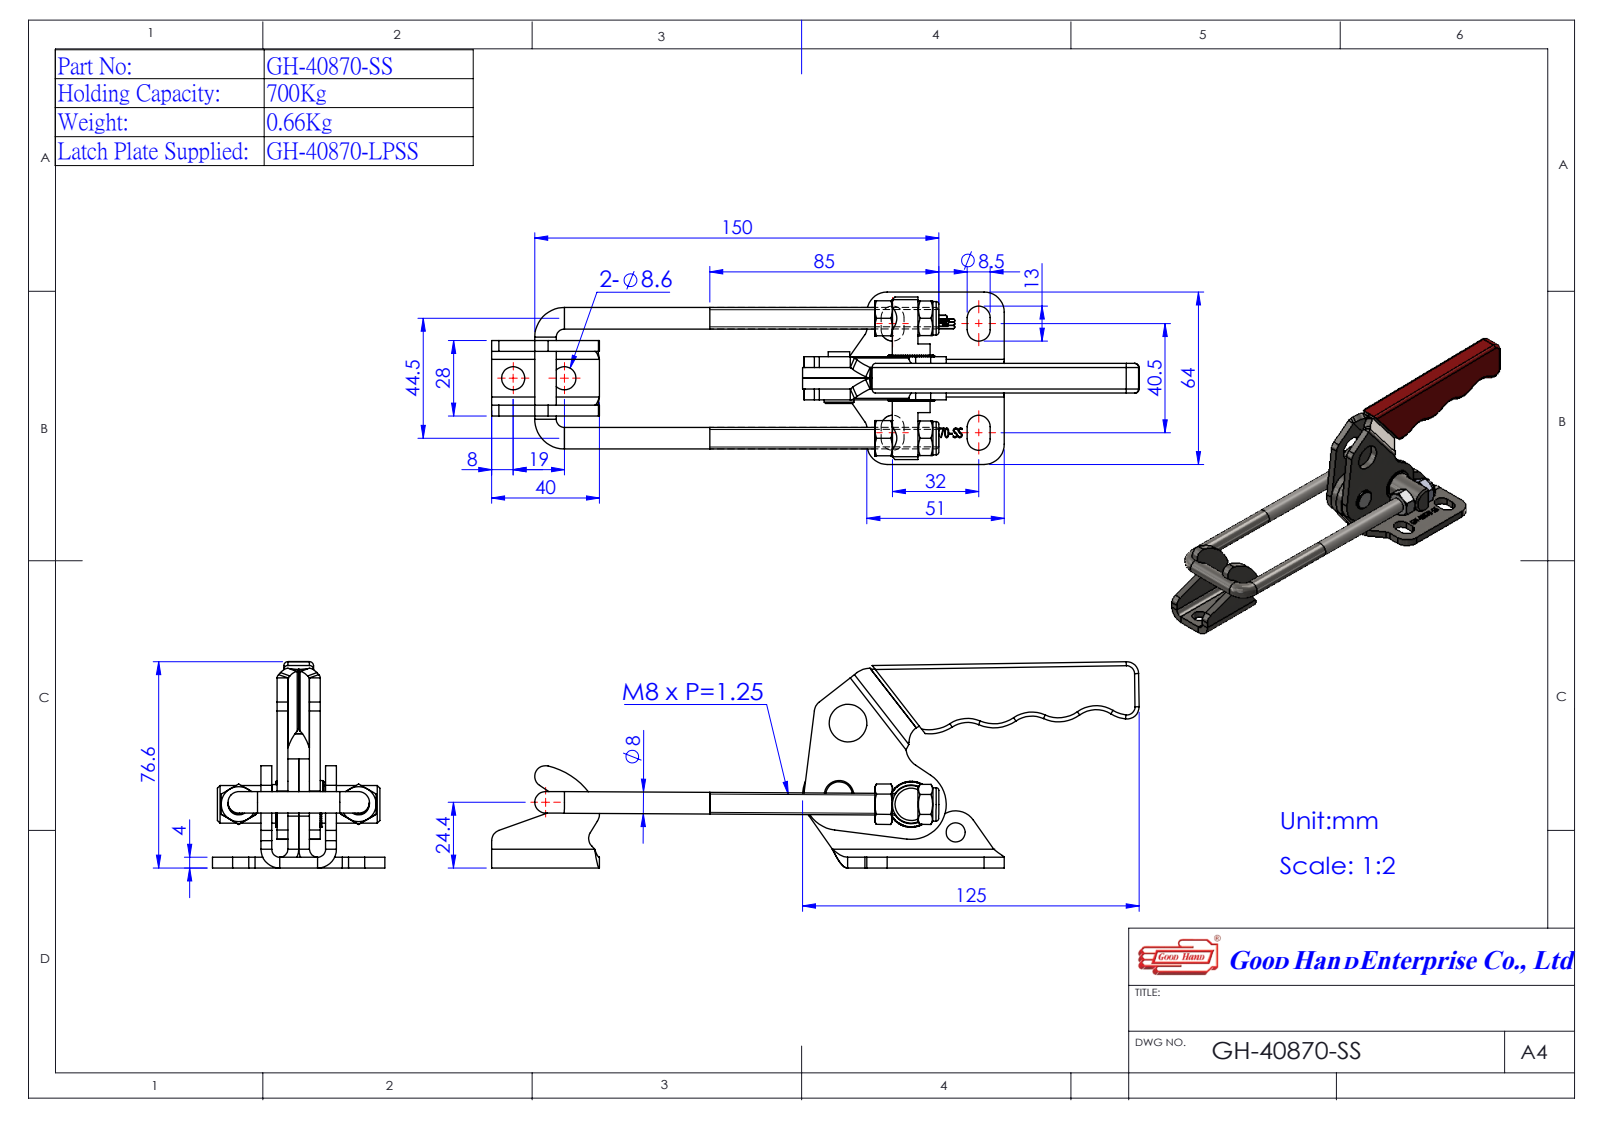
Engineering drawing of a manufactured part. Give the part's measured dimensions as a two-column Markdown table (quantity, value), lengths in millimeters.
| quantity | value |
| --- | --- |
| part name | 440870SS44-1^GH-40870-SS; GH-40870-SS; Group2^GH-40870-SS; Group1^GH-40870-SS (+2 more) |
| STEP written by | SolidWorks 2016 (AUTOMOTIVE_DESIGN) |
| units | millimeters |
| bodies | 8 solids, 783 faces (345 planar, 174 cylindrical, 264 other) |
| overall size | 238.21 × 82.48 × 64 |
| volume | 95 897 mm³ |
| surface area | 48 752 mm² |
| round holes (diameter × count) | 8 × 3, 3 × 2, 6.8 × 2, 8.5 × 2, 8.6 × 2, 9.4 × 2, 14 × 2, 1.53 × 1, 6.5 × 1, 7.1 × 1 |
| round bosses / shafts (diameter × count) | 12.4 × 2, 17 × 1, 11 × 1, 8 × 1, 7.95 × 1, 1.47 × 1 |
| partial cylindrical surfaces (radius × count) | 4.25 × 8, 4 × 5, 8.25 × 5, 4.01 × 4, 7.5 × 4, 0.58 × 3, 0.62 × 3, 8 × 3 |
| main face-to-face distances | 4, 9.5, 1.5, 2.5, 12, 13.5, 18, 8, 6, 11 |
| hole center spacings | 44.5, 27, 19, 20.23, 36.14, 38.19, 42.03, 45.43 |
